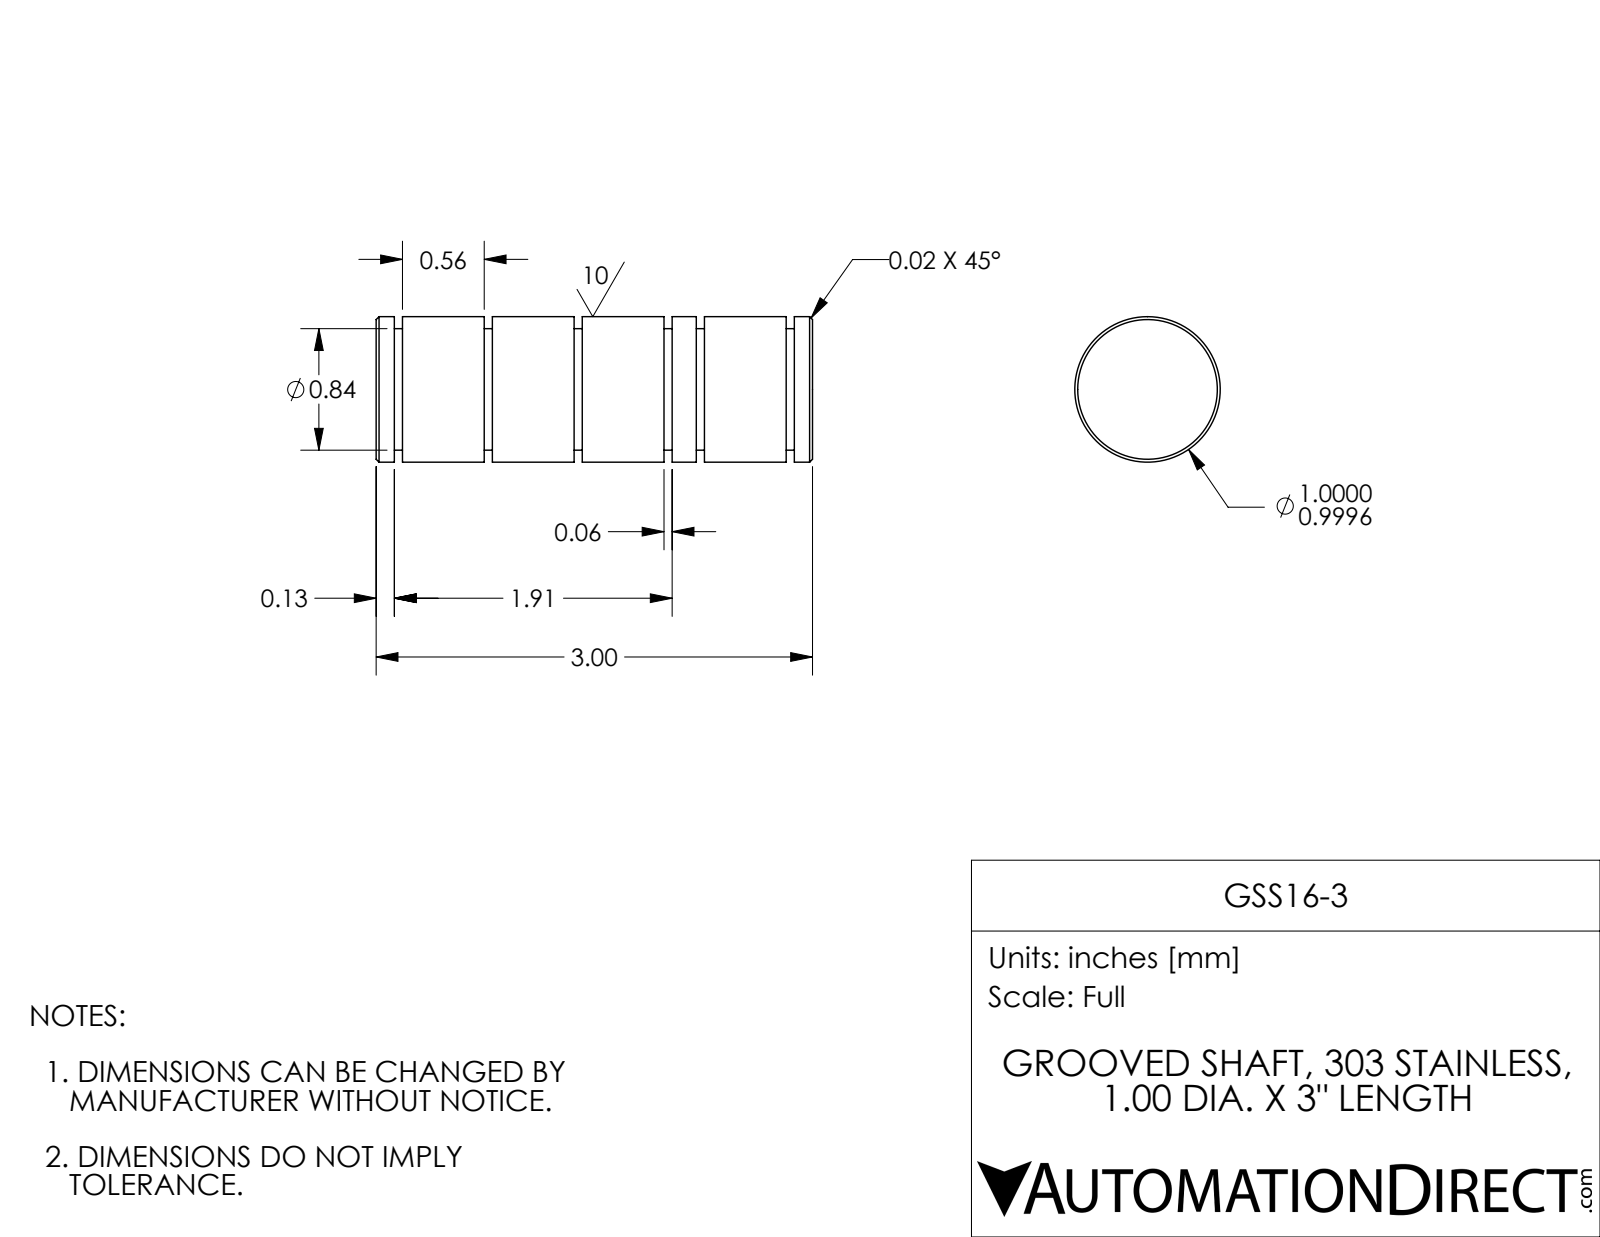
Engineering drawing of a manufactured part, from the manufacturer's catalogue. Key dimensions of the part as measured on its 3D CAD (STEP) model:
Part name (STEP PRODUCT): GSS16-3
STEP written by: SolidWorks 2017 (AUTOMOTIVE_DESIGN)
Units: inches
Bodies: 1 solid, 44 faces (14 planar, 26 cylindrical, 4 other)
Overall size (bounding box): 3 × 1 × 1
Volume: 2.275 in³ · Surface area: 13.6 in²
Round bosses / shafts (diameter × count): ⌀1 ×1, ⌀0.835 ×1
Main face-to-face distances: 0.618, 0.056, 3, 0.674, 1.236, 0.618, 2.076, 0.181, 0.743, 0.799
